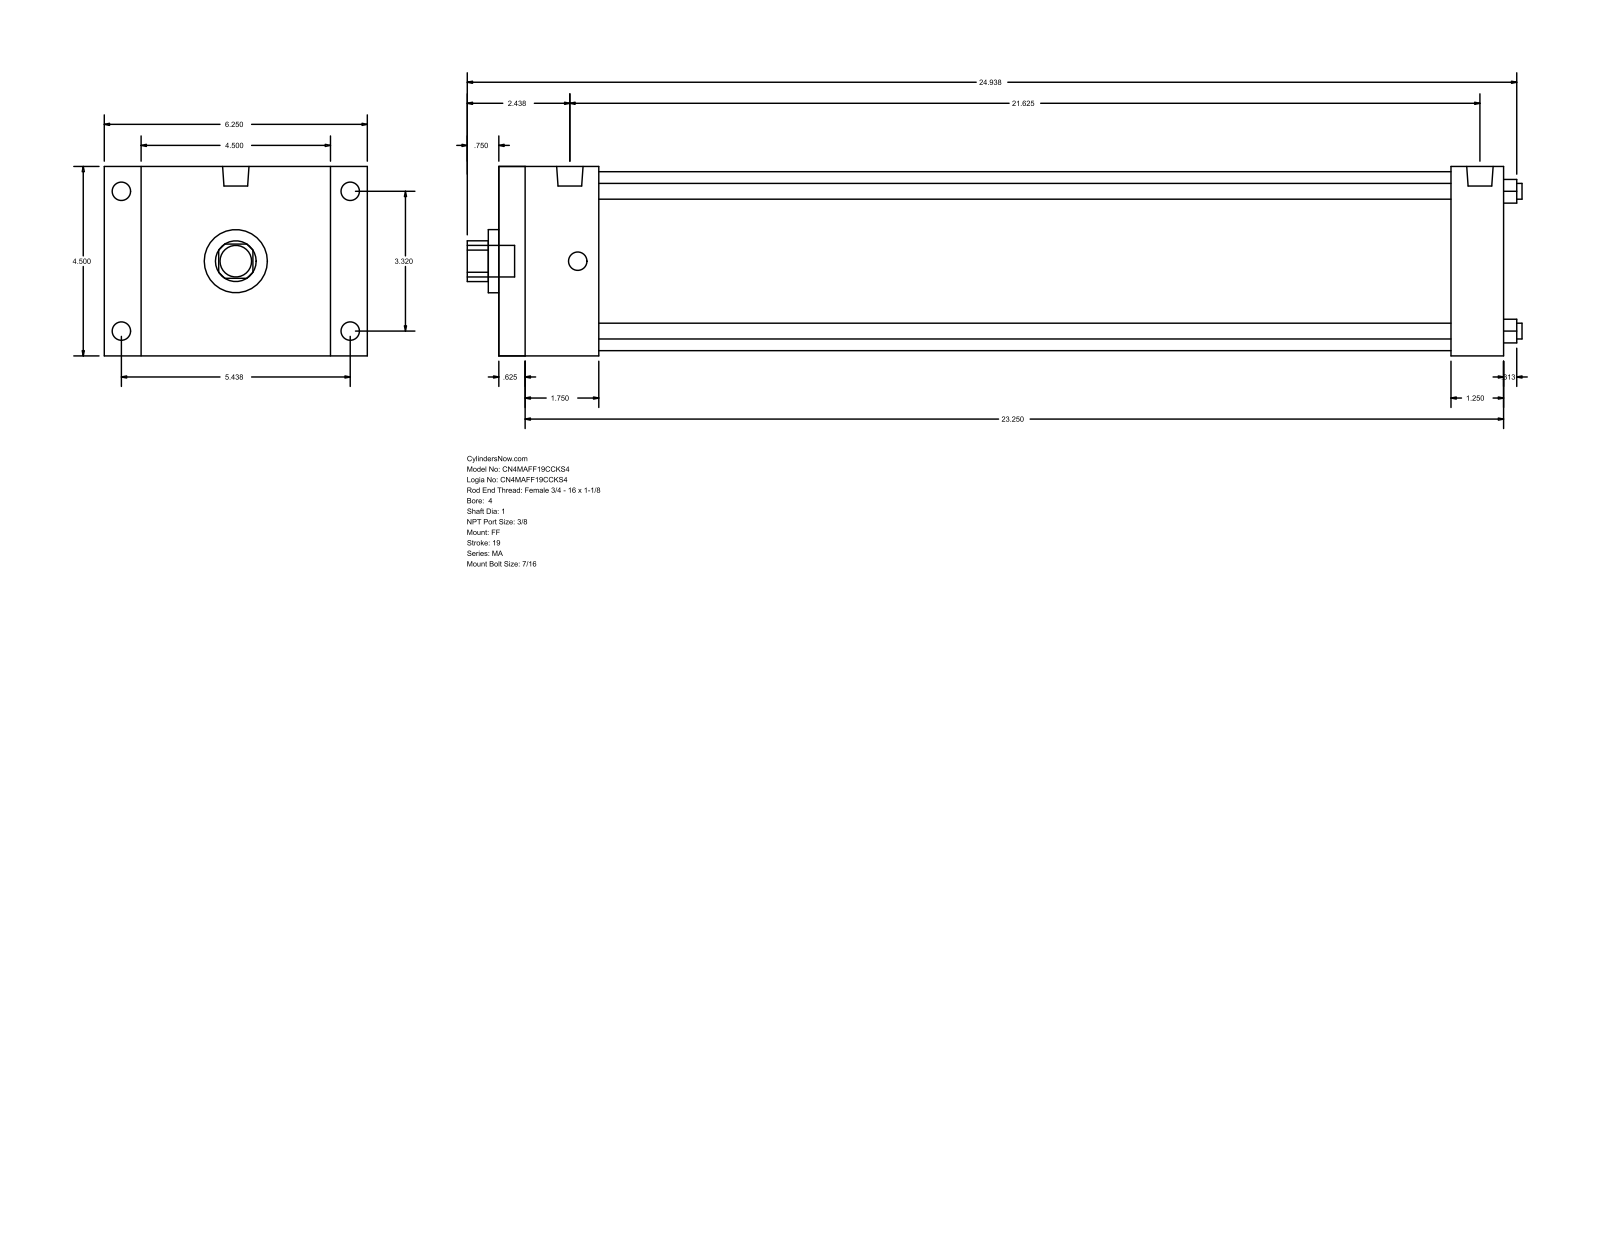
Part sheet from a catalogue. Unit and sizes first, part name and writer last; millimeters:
Units: millimetres
Overall size (bounding box): 636.59 × 158.75 × 114.3
Round holes (diameter × count): ⌀9.53 ×4, ⌀25.4 ×1, ⌀38.1 ×1, ⌀107.95 ×1
Round bosses / shafts (diameter × count): ⌀11.11 ×8, ⌀15.93 ×2, ⌀19.05 ×1
Partial cylindrical surfaces — rounded edges, fillets, slot ends (radius × count): R12.29 ×1
Main face-to-face distances: 114.3, 606.43, 15.87, 590.56, 22.23, 136.53, 574.68, 558.81, 31.75, 60.33
Hole centre spacings: 59.62, 84.32, 119.25
Bodies: 0 solids, 92 faces (64 planar, 28 cylindrical, 0 other)
Part name (STEP PRODUCT): MA_FF__0400_1
STEP written by: GSSL Pune (CONFIG_CONTROL_DESIGN)
